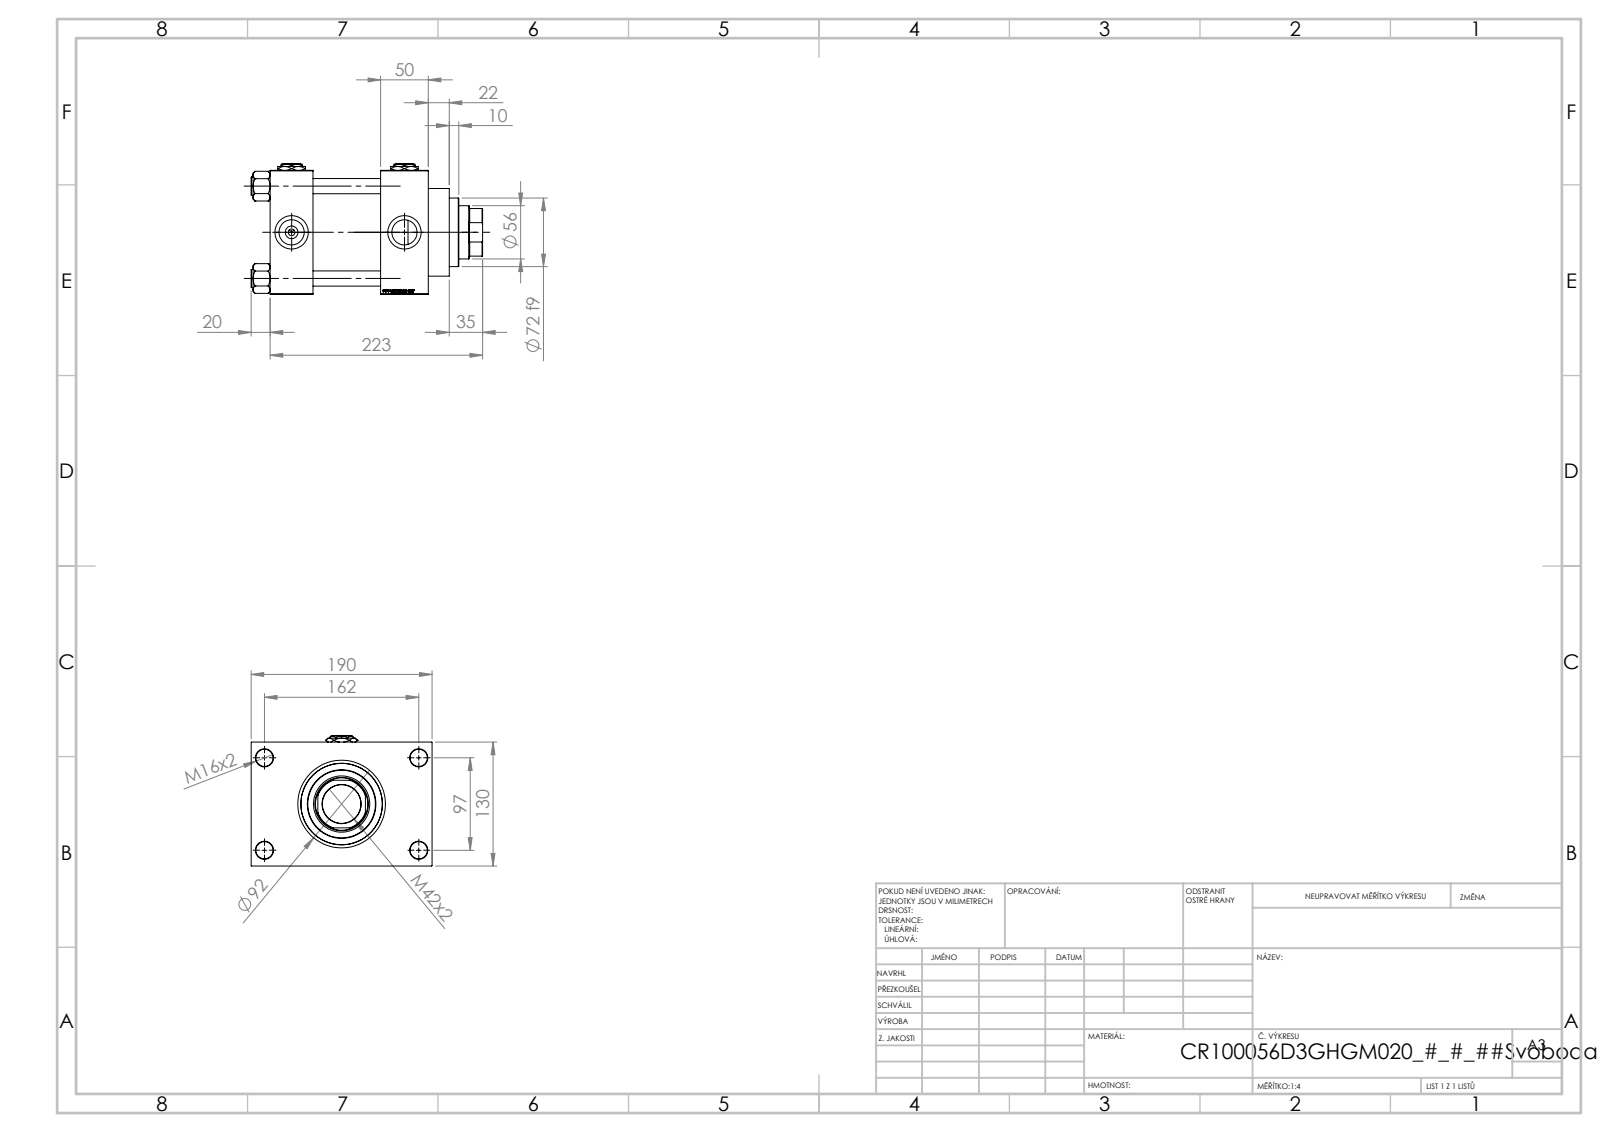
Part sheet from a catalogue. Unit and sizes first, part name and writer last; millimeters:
Units: millimetres
Overall size (bounding box): 243 × 190 × 137
Round holes (diameter × count): ⌀16 ×4, ⌀18 ×4, ⌀26.44 ×4, ⌀35 ×4, ⌀7 ×3, ⌀40.5 ×1, ⌀56 ×1, ⌀59 ×1, ⌀76 ×1, ⌀85.5 ×1, ⌀100 ×1
Round bosses / shafts (diameter × count): ⌀19 ×4, ⌀106 ×1, ⌀92 ×1, ⌀72 ×1
Partial cylindrical surfaces — rounded edges, fillets, slot ends (radius × count): R27 ×1
Main face-to-face distances: 130, 116, 50, 45, 71, 121, 166, 30, 160, 20
Hole centre spacings: 32.55, 68.52, 94.41, 96.9, 102.27, 129.45, 161.73, 97
Volume: 2 614 000 mm³ · Surface area: 369 282 mm²
Bodies: 13 solids, 1252 faces (593 planar, 99 cylindrical, 560 other)
Part name (STEP PRODUCT): V215CR_D_TYCINKA; V215_VC_A; V215CR_VCP_D; Zatka_pro_OIL_PORT (+2 more)
STEP written by: SolidWorks 2019 (CONFIG_CONTROL_DESIGN)
